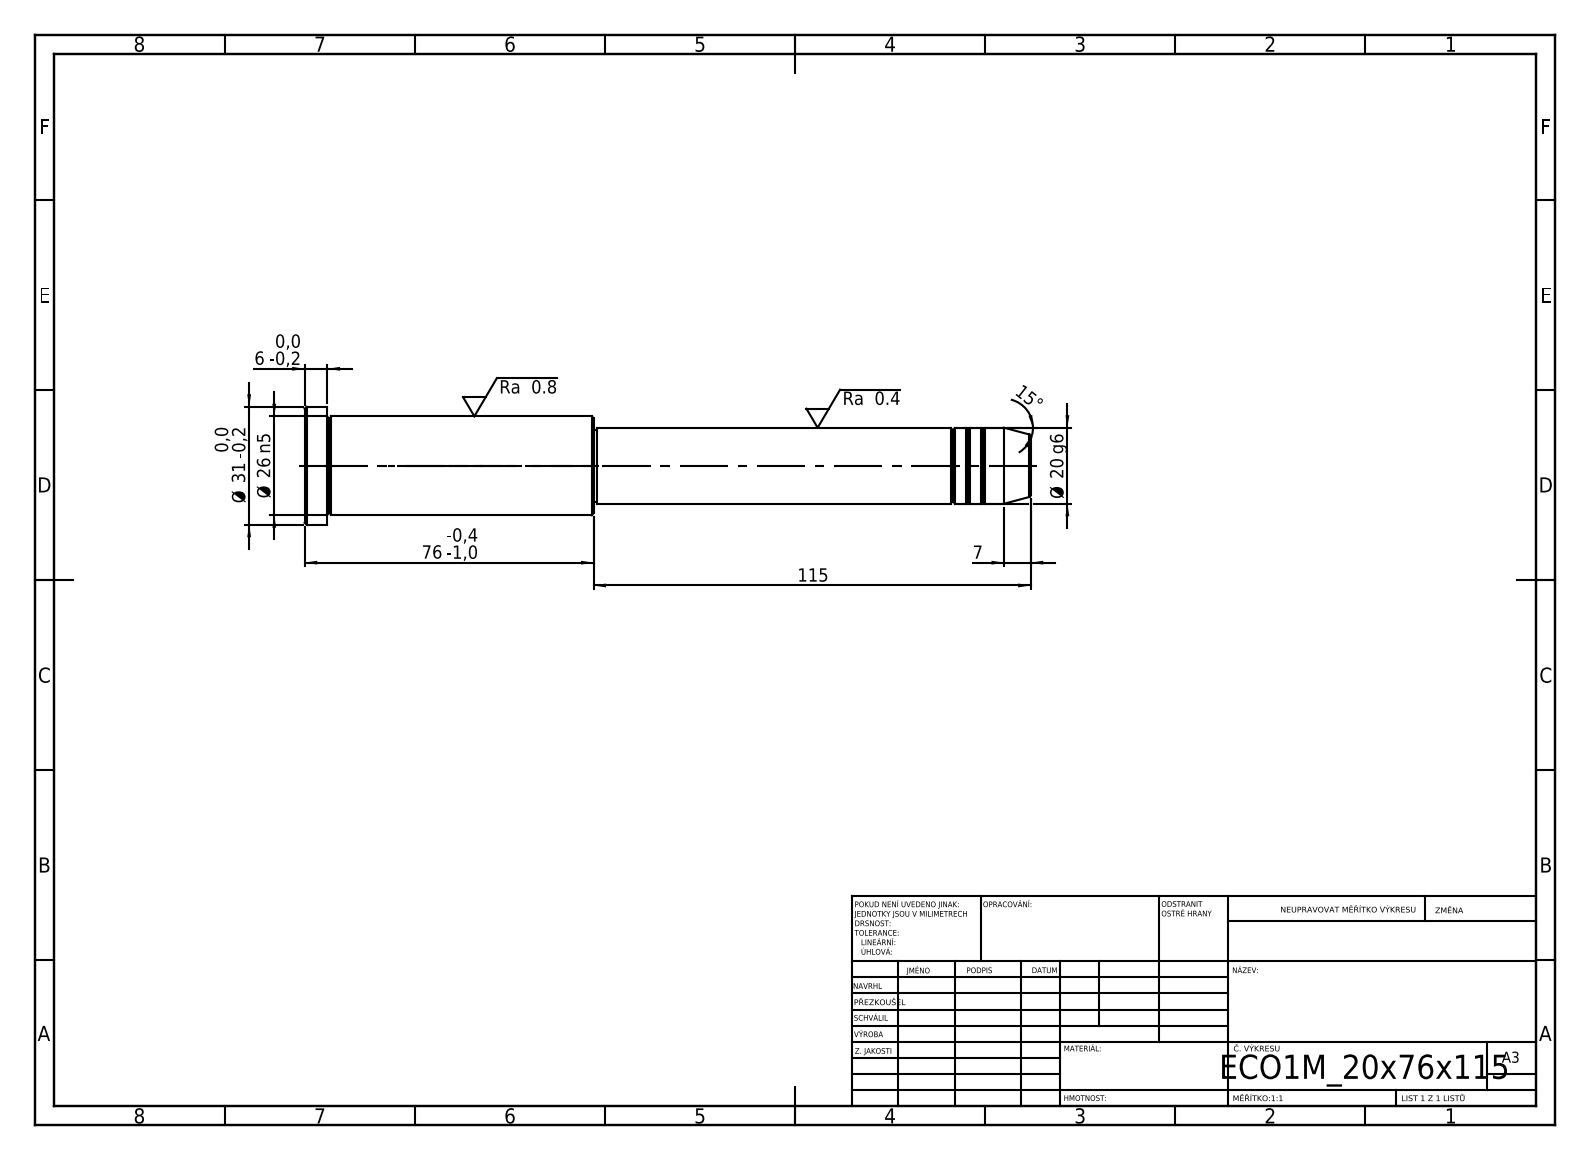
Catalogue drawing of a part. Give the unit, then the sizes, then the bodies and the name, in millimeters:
Units: millimetres
Overall size (bounding box): 191 × 31 × 31
Round bosses / shafts (diameter × count): ⌀31 ×1, ⌀26 ×1, ⌀20 ×1, ⌀19 ×1
Main face-to-face distances: 6, 70, 76, 115, 185, 191, 114, 1, 71, 77
Volume: 77 277 mm³ · Surface area: 15 044 mm²
Bodies: 1 solid, 43 faces (5 planar, 14 cylindrical, 24 other)
STEP written by: SolidWorks 2019 (CONFIG_CONTROL_DESIGN)
